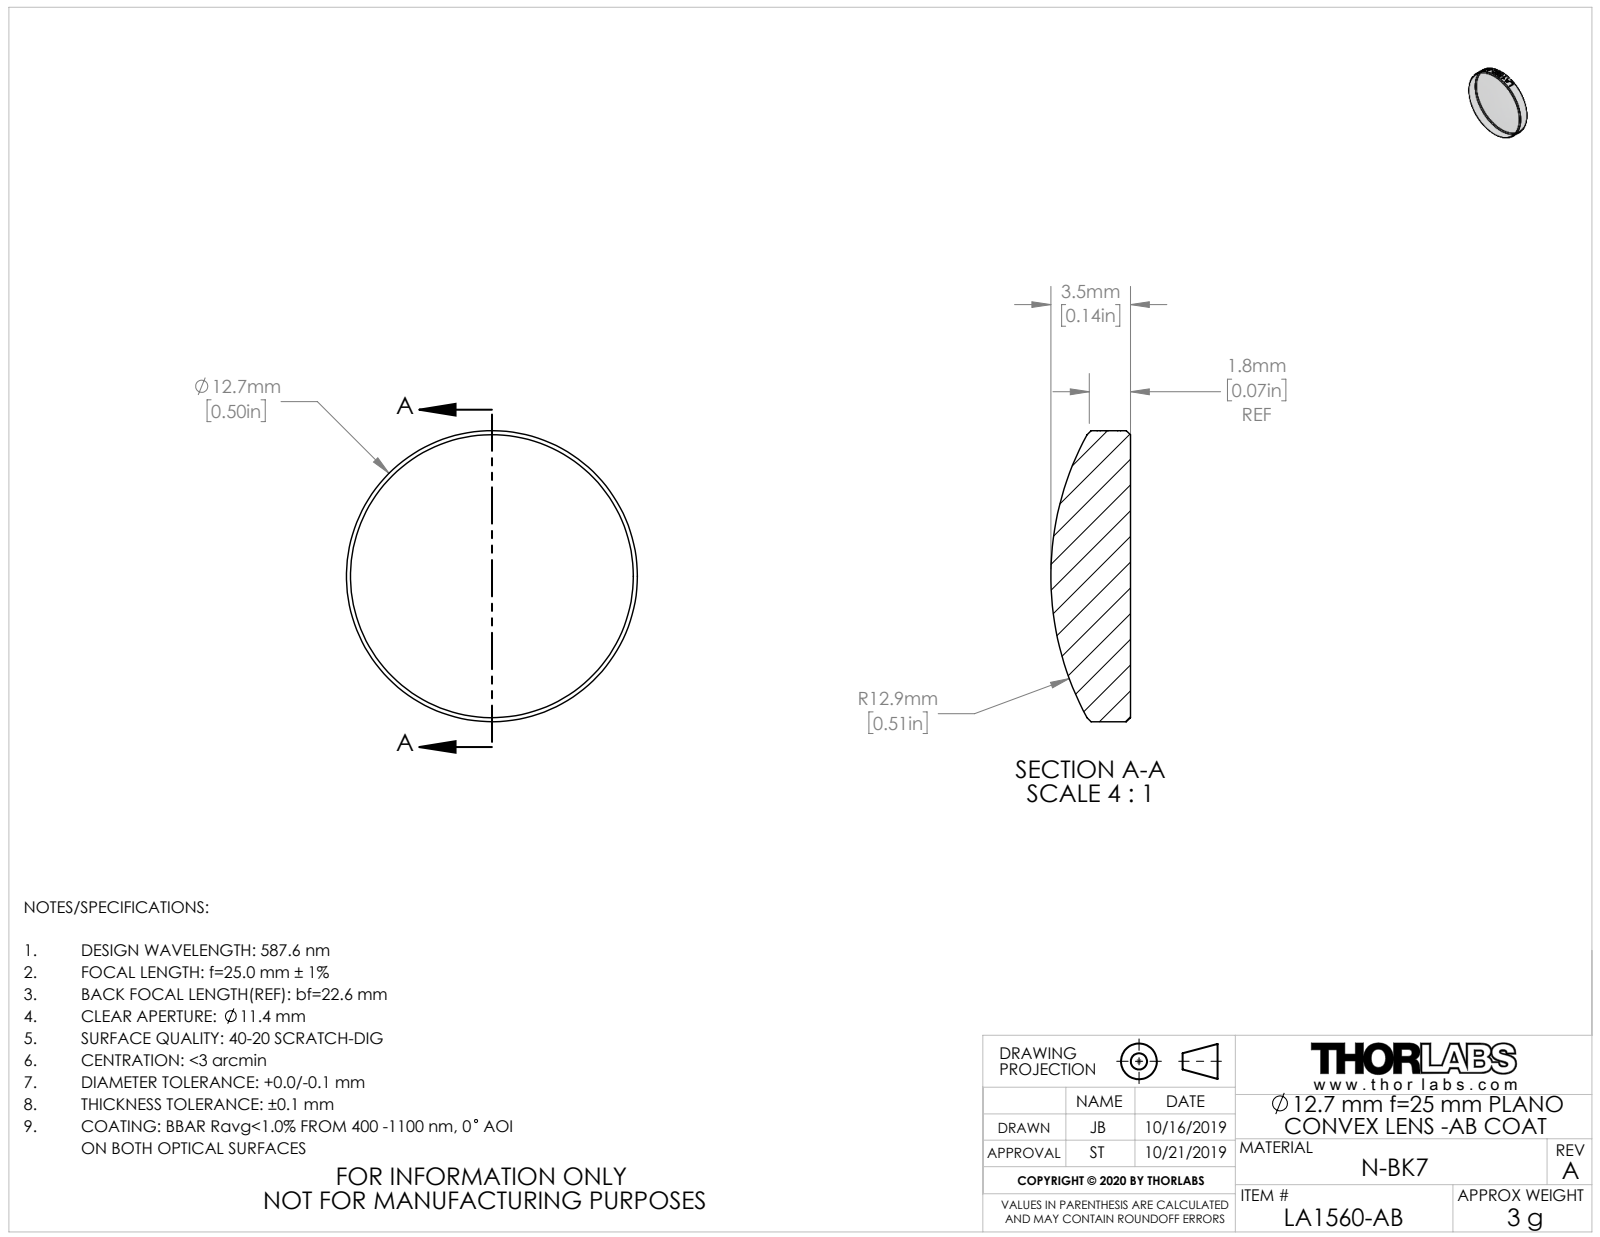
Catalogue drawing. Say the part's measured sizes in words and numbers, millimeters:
The part is named "TTN195795-E0W". Its 3-D file was written by "SolidWorks 2018 (CONFIG_CONTROL_DESIGN)". It is 1 solid with 28 faces: 1 planar, 21 cylindrical and 6 other. Overall it measures 12.7 by 12.7 by 3.47 millimeters. Its volume is 335 cubic millimeters and its surface area 328 square millimeters. Round bosses or shafts: 1 of diameter 12.7.
